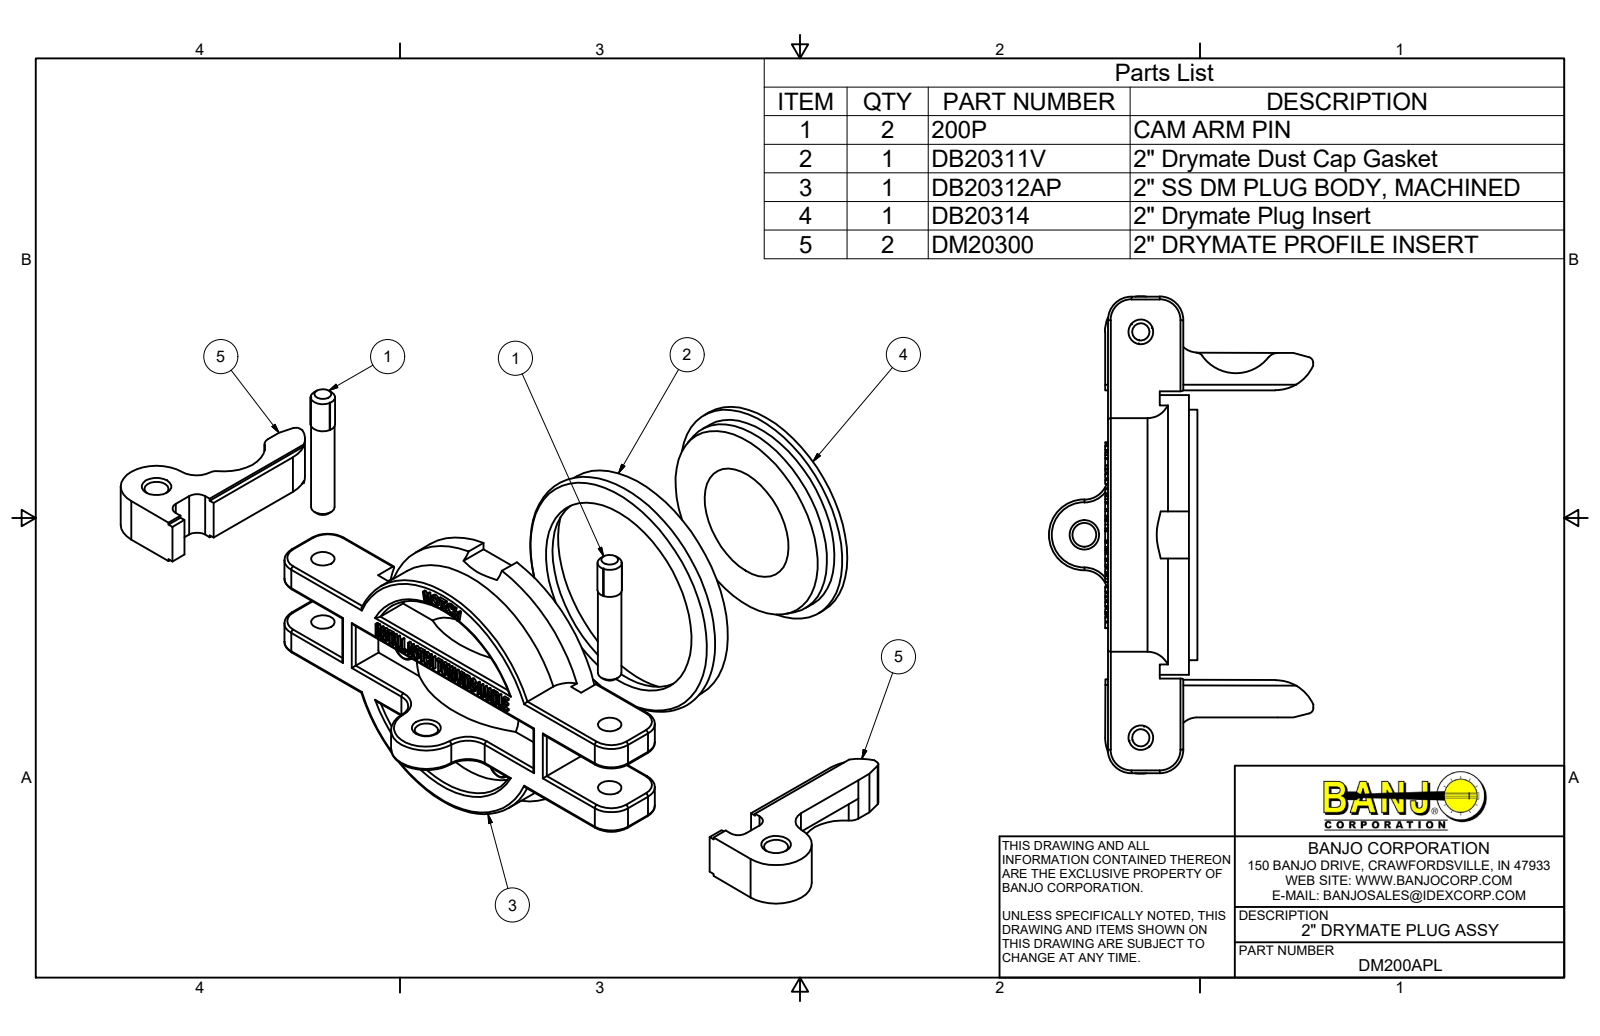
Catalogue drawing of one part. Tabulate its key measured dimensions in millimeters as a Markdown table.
| quantity | value |
| --- | --- |
| part name | DB20312AX; DB20312AY; DB20312AP; DB20311V (+4 more) |
| STEP written by | Autodesk Inventor 2016 (AUTOMOTIVE_DESIGN) |
| units | millimeters |
| bodies | 7 solids, 668 faces (383 planar, 110 cylindrical, 175 other) |
| overall size | 128.78 × 74.9 × 71.28 |
| volume | 104 905 mm³ |
| surface area | 48 322 mm² |
| round holes (diameter × count) | 3.17 × 3, 6.35 × 3, 6.5 × 2, 55.58 × 1, 61.93 × 1, 67.56 × 1 |
| round bosses / shafts (diameter × count) | 7.11 × 3, 6.6 × 2, 6.32 × 2, 75.44 × 1, 69.09 × 1, 61.72 × 1, 55.75 × 1 |
| partial cylindrical surfaces (radius × count) | 0.76 × 20, 6.35 × 6, 3.05 × 4, 1.52 × 2, 2.03 × 2, 3.17 × 2, 5.59 × 2, 9.65 × 2 |
| main face-to-face distances | 7.57, 20.87, 7.87, 5.59, 1.98, 20.57, 13, 14.27, 21.84, 16.25 |
| hole center spacings | 24.13, 41.8, 56.82, 41.79, 109.48 |
